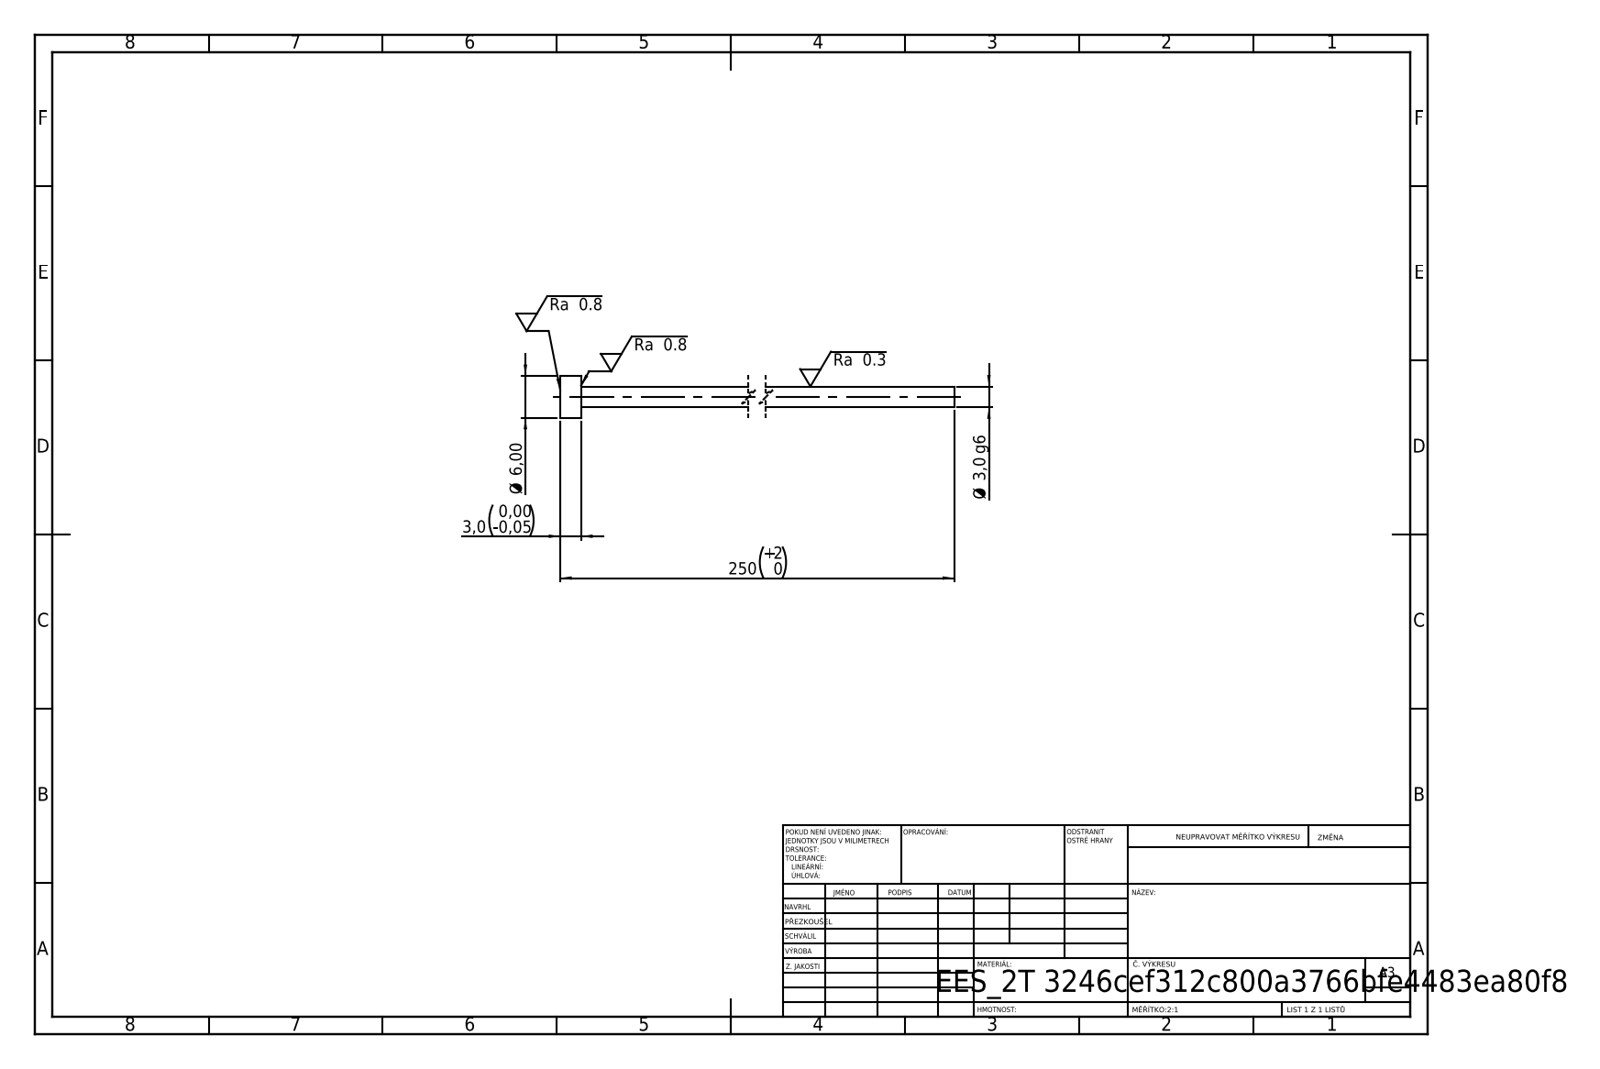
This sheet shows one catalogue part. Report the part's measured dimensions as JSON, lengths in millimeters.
{"step_written_by": "SolidWorks 2019 (CONFIG_CONTROL_DESIGN)", "units": "millimeters", "bodies": {"solids": 1, "faces": 7, "planar": 3, "cylindrical": 4, "other": 0}, "overall_size": [250, 6, 6], "volume_mm3": 1831, "surface_area_mm2": 2441, "round_bosses_or_shafts": [[6, 1], [3, 1]], "face_to_face_distances": [3, 250, 247]}
